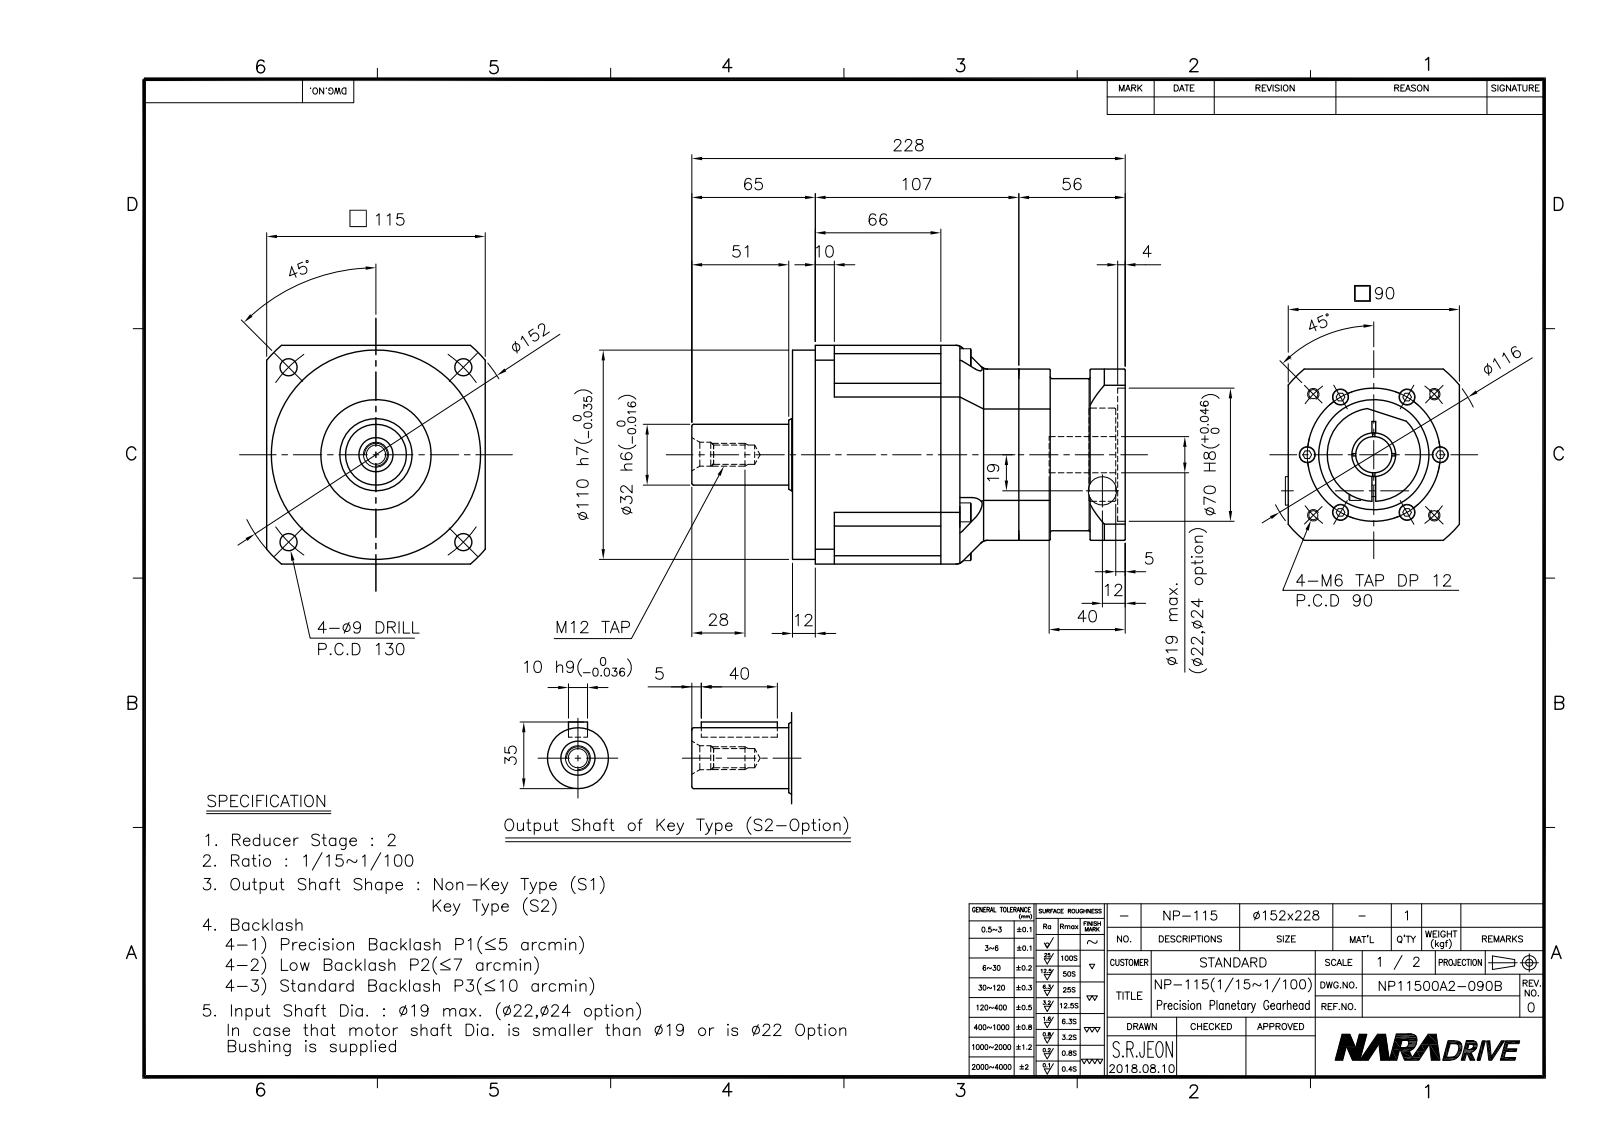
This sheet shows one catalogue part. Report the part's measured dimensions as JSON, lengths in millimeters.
{"part_name": "NP11500A2-090B-S1", "step_written_by": "Autodesk Inventor 2015 (AUTOMOTIVE_DESIGN)", "units": "millimeters", "bodies": {"solids": 2, "faces": 558, "planar": 255, "cylindrical": 159, "other": 144}, "overall_size": [228, 115, 115], "volume_mm3": 1213000, "surface_area_mm2": 164389, "round_holes": [[9, 14], [4.13, 10], [5.5, 10], [4.92, 9], [6.6, 5], [7, 1], [8.5, 1], [10.11, 1], [10.25, 1], [19, 1], [23, 1], [58, 1]], "round_bosses_or_shafts": [[8.5, 10], [5, 10], [10, 5], [6, 5], [110, 1], [79, 1], [49, 1], [38, 1]], "partial_cylinders_radius": [[0.5, 16], [5, 8], [12.5, 8], [5.5, 1], [35, 1], [51, 1], [58, 1], [65, 1]], "face_to_face_distances": [102.5, 12.5, 68, 115, 10, 56, 107, 78, 90, 2], "hole_center_spacings": [35, 110.01, 12.5, 14.4, 17.38, 23.82, 31.98, 35.01]}
